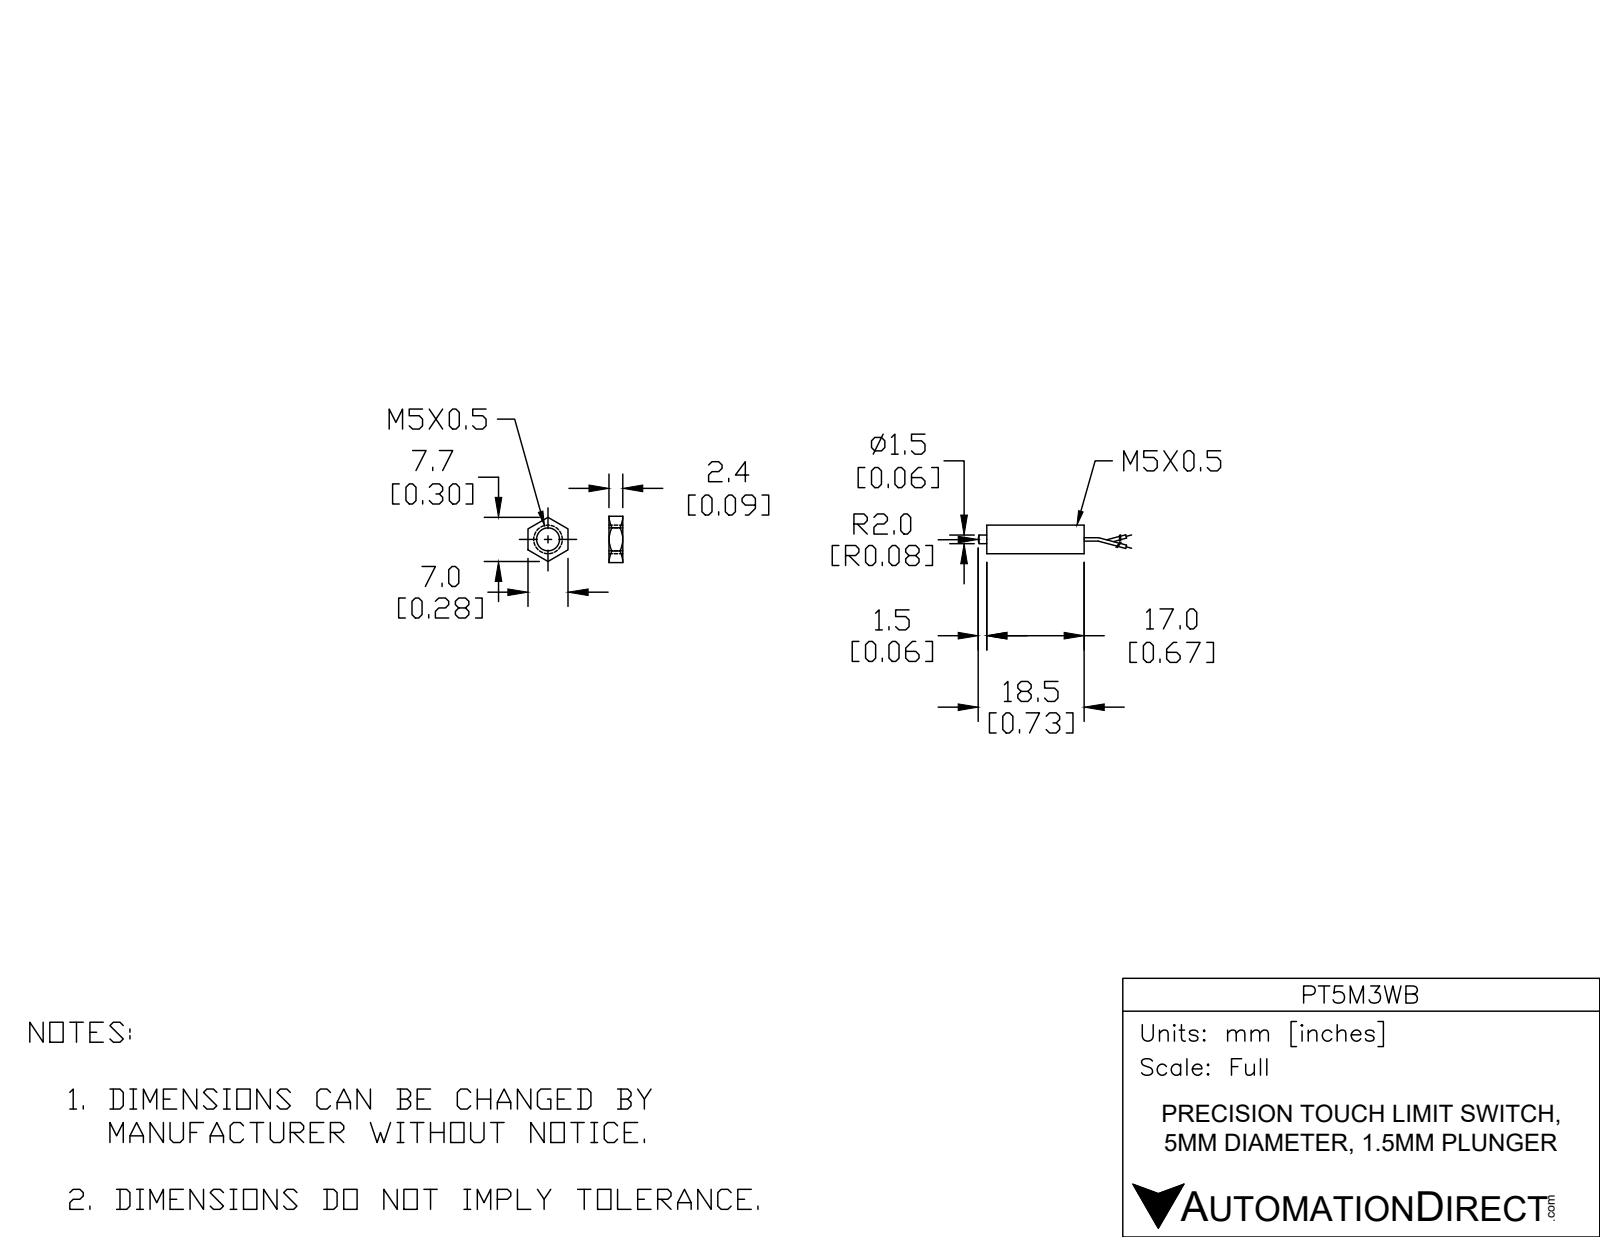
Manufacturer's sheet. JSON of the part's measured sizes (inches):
{"step_written_by": "Spatial InterOp 3D (CONFIG_CONTROL_DESIGN)", "units": "inches", "bodies": {"solids": 1, "faces": 84, "planar": 4, "cylindrical": 75, "other": 5}, "overall_size": [1.122, 0.197, 0.197], "volume_in3": 0.018, "surface_area_in2": 0.795, "round_bosses_or_shafts": [[0.024, 2], [0.197, 1], [0.059, 1]], "face_to_face_distances": [0.669, 1.063, 0.394]}
